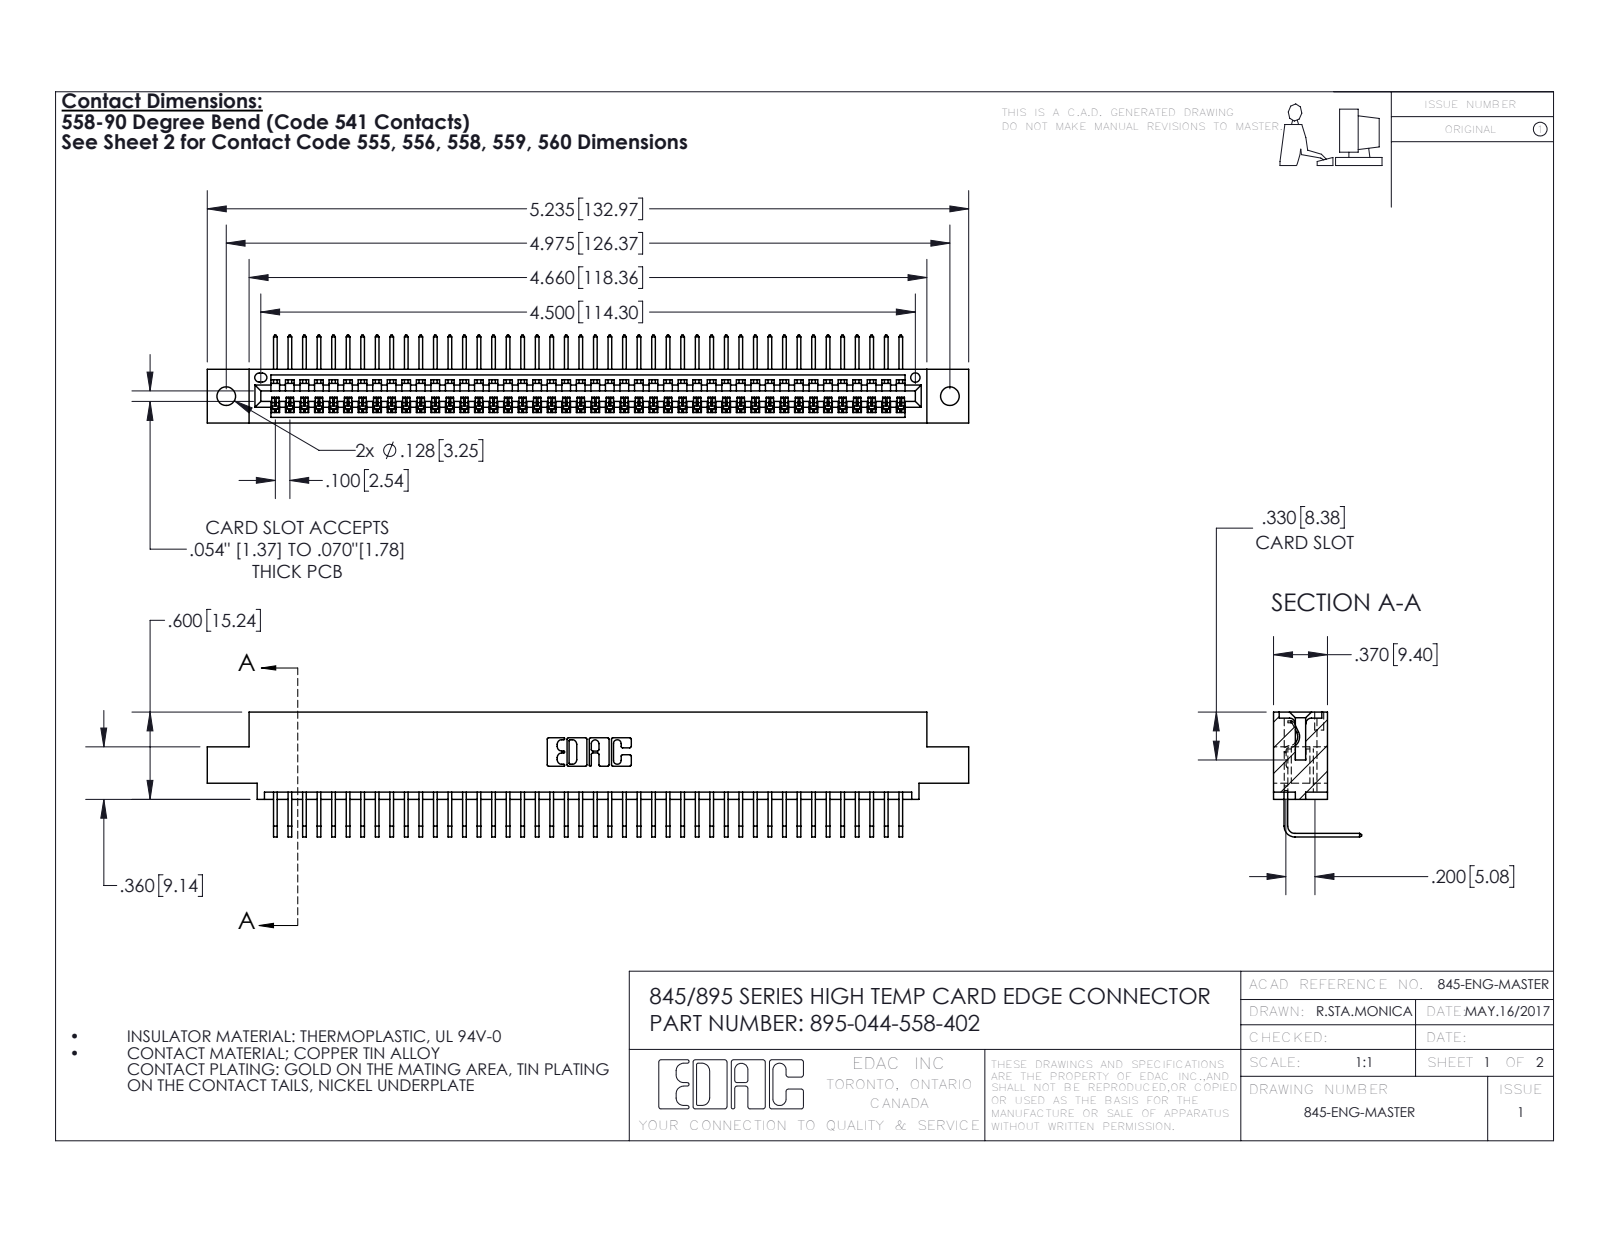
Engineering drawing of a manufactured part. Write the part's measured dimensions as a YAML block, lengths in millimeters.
part_name: "395-044-558-402; 345-292-001_558 Tail - 2; 345 Part_0.110 Offset - 0.128 Dia"
step_written_by: "SolidWorks 2016 (CONFIG_CONTROL_DESIGN)"
units: millimeters
bodies: {solids: 45, faces: 2770, planar: 1932, cylindrical: 838, other: 0}
overall_size: [133, 21.8, 15.4]
volume: 12700
surface_area: 17550
round_holes:
  - {diameter: 3.3, count: 2}
  - {diameter: 1.6, count: 1}
partial_cylinders:
  - {radius: 0.2, count: 88}
  - {radius: 0.3, count: 22}
  - {radius: 0.2, count: 6}
  - {radius: 0.8, count: 6}
  - {radius: 0.7, count: 3}
  - {radius: 0.8, count: 2}
  - {radius: 1, count: 2}
  - {radius: 0.4, count: 1}
face_to_face_distances: [1.8, 7.6, 9.4, 5.1, 2.5, 6.9, 0.6, 5.7, 3.8, 1.8]
hole_center_spacings: [6.9, 120.4, 126.4]
